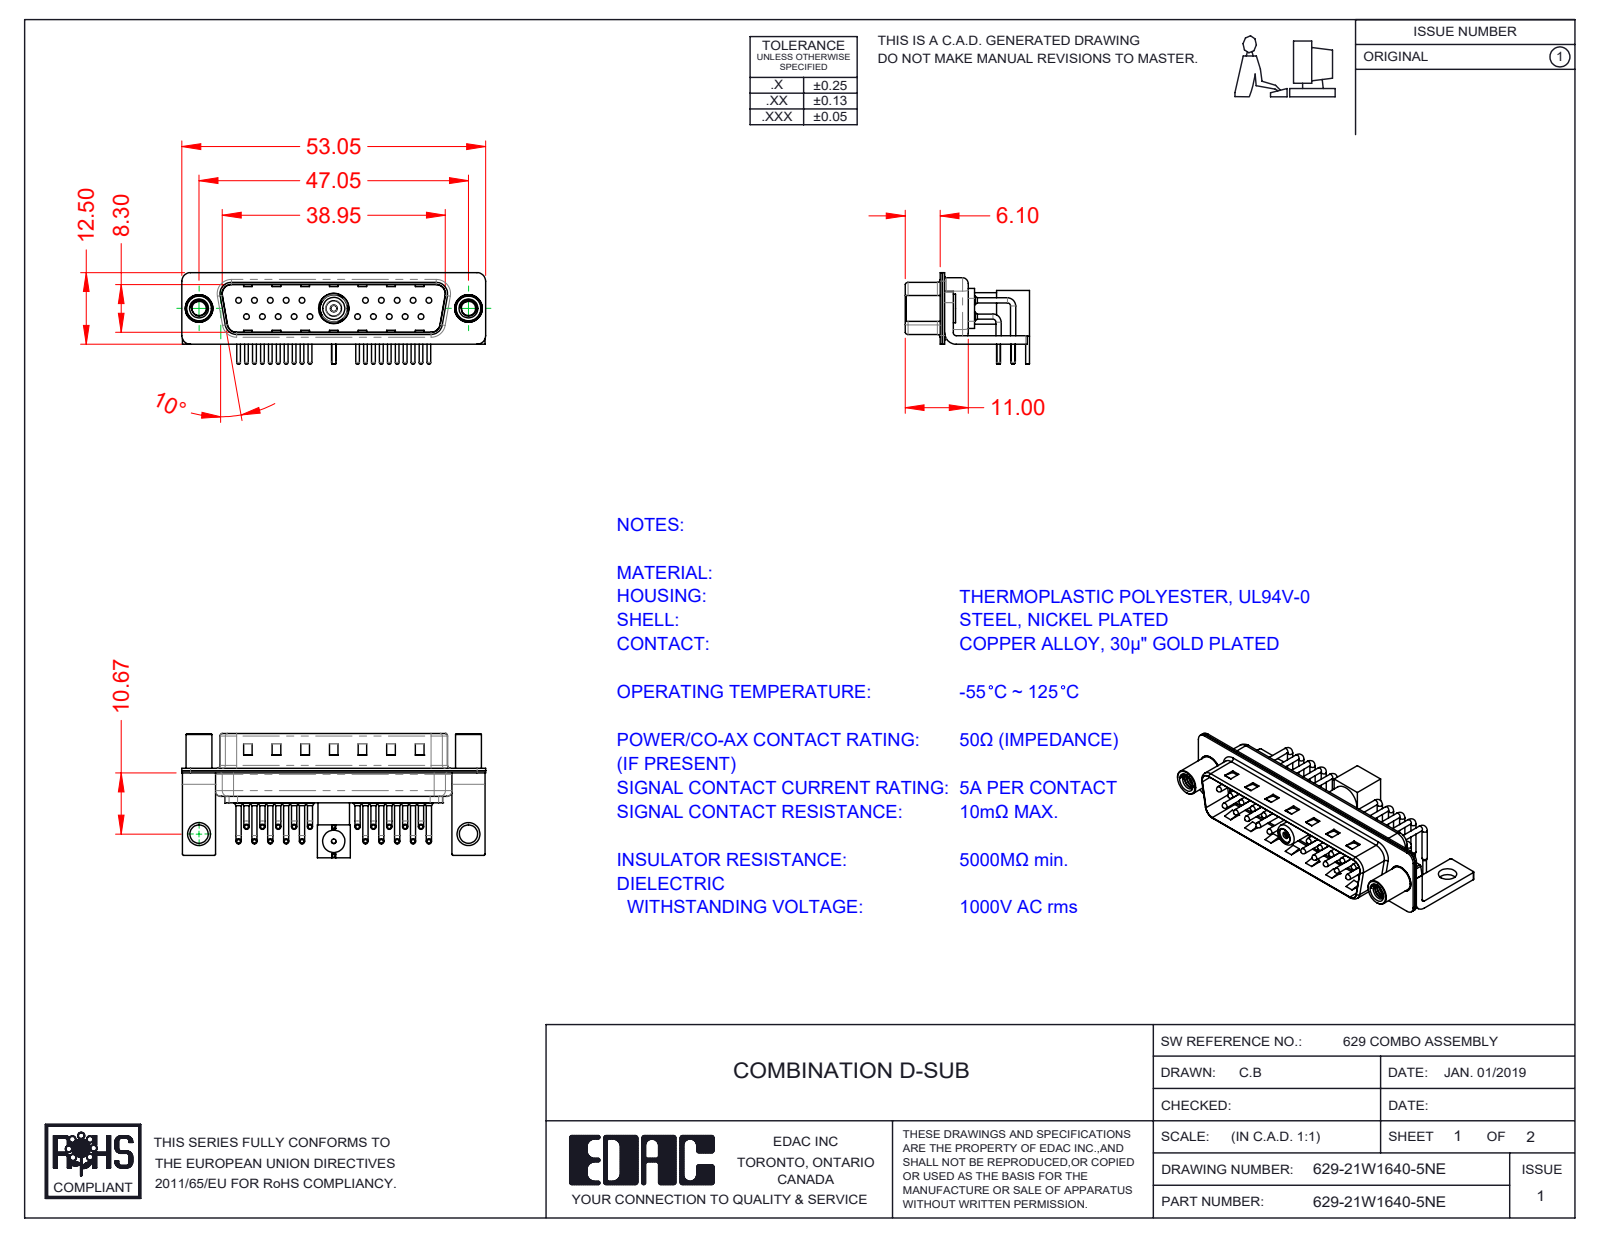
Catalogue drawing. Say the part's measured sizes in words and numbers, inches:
The part is named "629Combo Shell Rear_25 Contacts; 629-21W1640-5NE; Co-Ax Jack Assy_RA; Socket_RA (+8 more)". Its 3-D file was written by "SolidWorks 2020 (CONFIG_CONTROL_DESIGN)". It is 34 solids with 2826 faces: 1530 planar, 996 cylindrical and 300 other. Overall it measures 2.089 by 0.855 by 0.63 inches. Its volume is 0.217 cubic inches and its surface area 14.51 square inches. Round holes: 21 of diameter 0.063, 20 of diameter 0.03, 20 of diameter 0.079, 3 of diameter 0.098, 2 of diameter 0.126, 2 of diameter 0.157, 2 of diameter 0.189, 1 of diameter 0.031, 1 of diameter 0.043, 1 of diameter 0.047, 1 of diameter 0.059, 1 of diameter 0.106. Round bosses or shafts: 40 of diameter 0.035, 20 of diameter 0.059, 20 of diameter 0.039, 20 of diameter 0.026, 2 of diameter 0.197, 2 of diameter 0.193, 2 of diameter 0.177, 2 of diameter 0.031. Partial cylindrical surfaces (rounded edges, fillets, slot ends): 20 of radius 0.04, 16 of radius 0.01, 16 of radius 0.059, 13 of radius 0.079, 9 of radius 0.02, 8 of radius 0.063, 4 of radius 0.024, 4 of radius 0.026. The main face-to-face distances are 0.016, 0.031, 0.374, 0.358, 0.059, 0.343, 0.39, 0.024, 0.014, 0.083. The hole center spacings are 0.124, 0.109, 0.218, 0.327, 0.198, 0.763, 0.826, 0.872.
